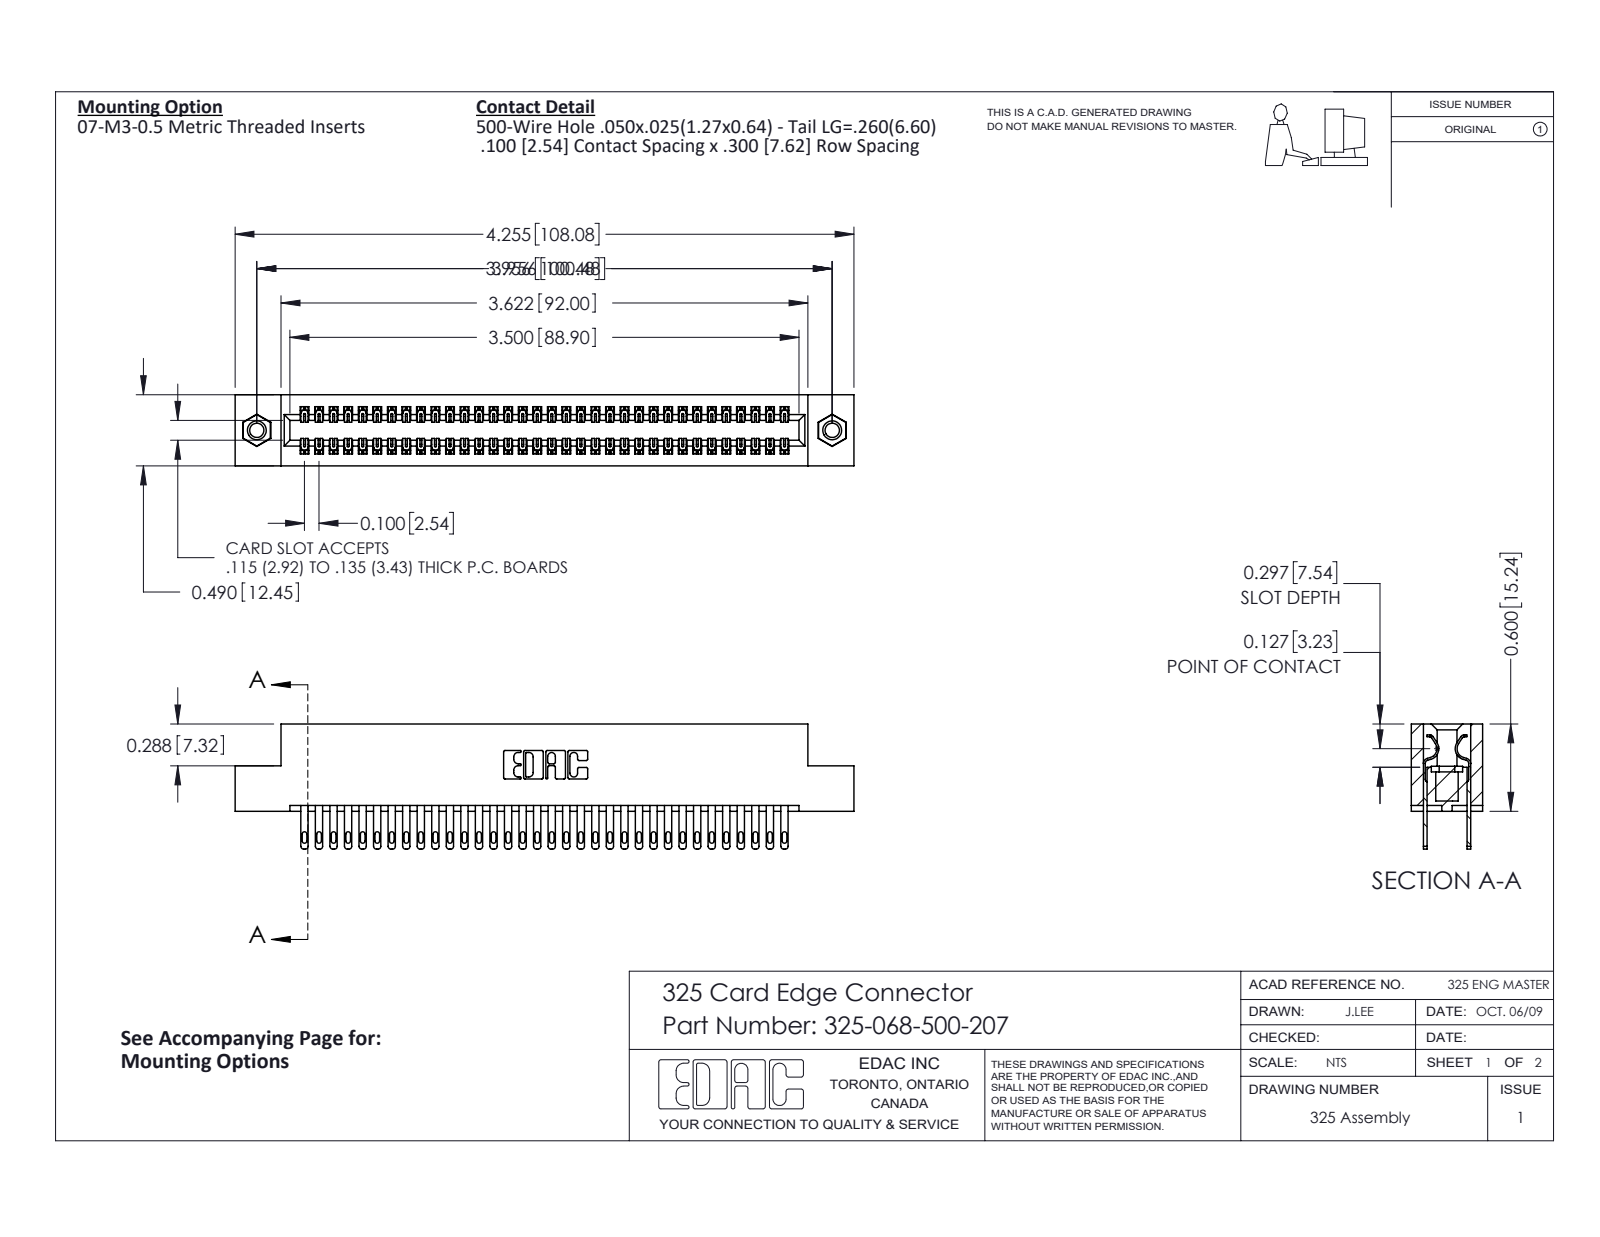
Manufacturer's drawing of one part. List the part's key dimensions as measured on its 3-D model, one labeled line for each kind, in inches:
Part name (STEP PRODUCT): 325-068-500-207; 345-250-001_345-250-005-103; 325 Part_TI; 325-292-001_325-293-100
STEP written by: SolidWorks 2016 (CONFIG_CONTROL_DESIGN)
Units: inches
Bodies: 71 solids, 3438 faces (2142 planar, 1280 cylindrical, 16 other)
Overall size (bounding box): 4.255 × 0.86 × 0.49
Volume: 0.859 in³ · Surface area: 27.25 in²
Round holes (diameter × count): ⌀0.098 ×2, ⌀0.125 ×2, ⌀0.16 ×2
Round bosses / shafts (diameter × count): ⌀0.155 ×2
Partial cylindrical surfaces — rounded edges, fillets, slot ends (radius × count): R0.006 ×102, R0.016 ×68, R0.02 ×68, R0.01 ×22, R0.007 ×6, R0.031 ×6, R0.026 ×3, R0.014 ×2
Main face-to-face distances: 0.083, 0.407, 0.3, 0.107, 0.383, 0.025, 0.49, 0.325, 0.275, 0.04
Hole centre spacings: 3.956
